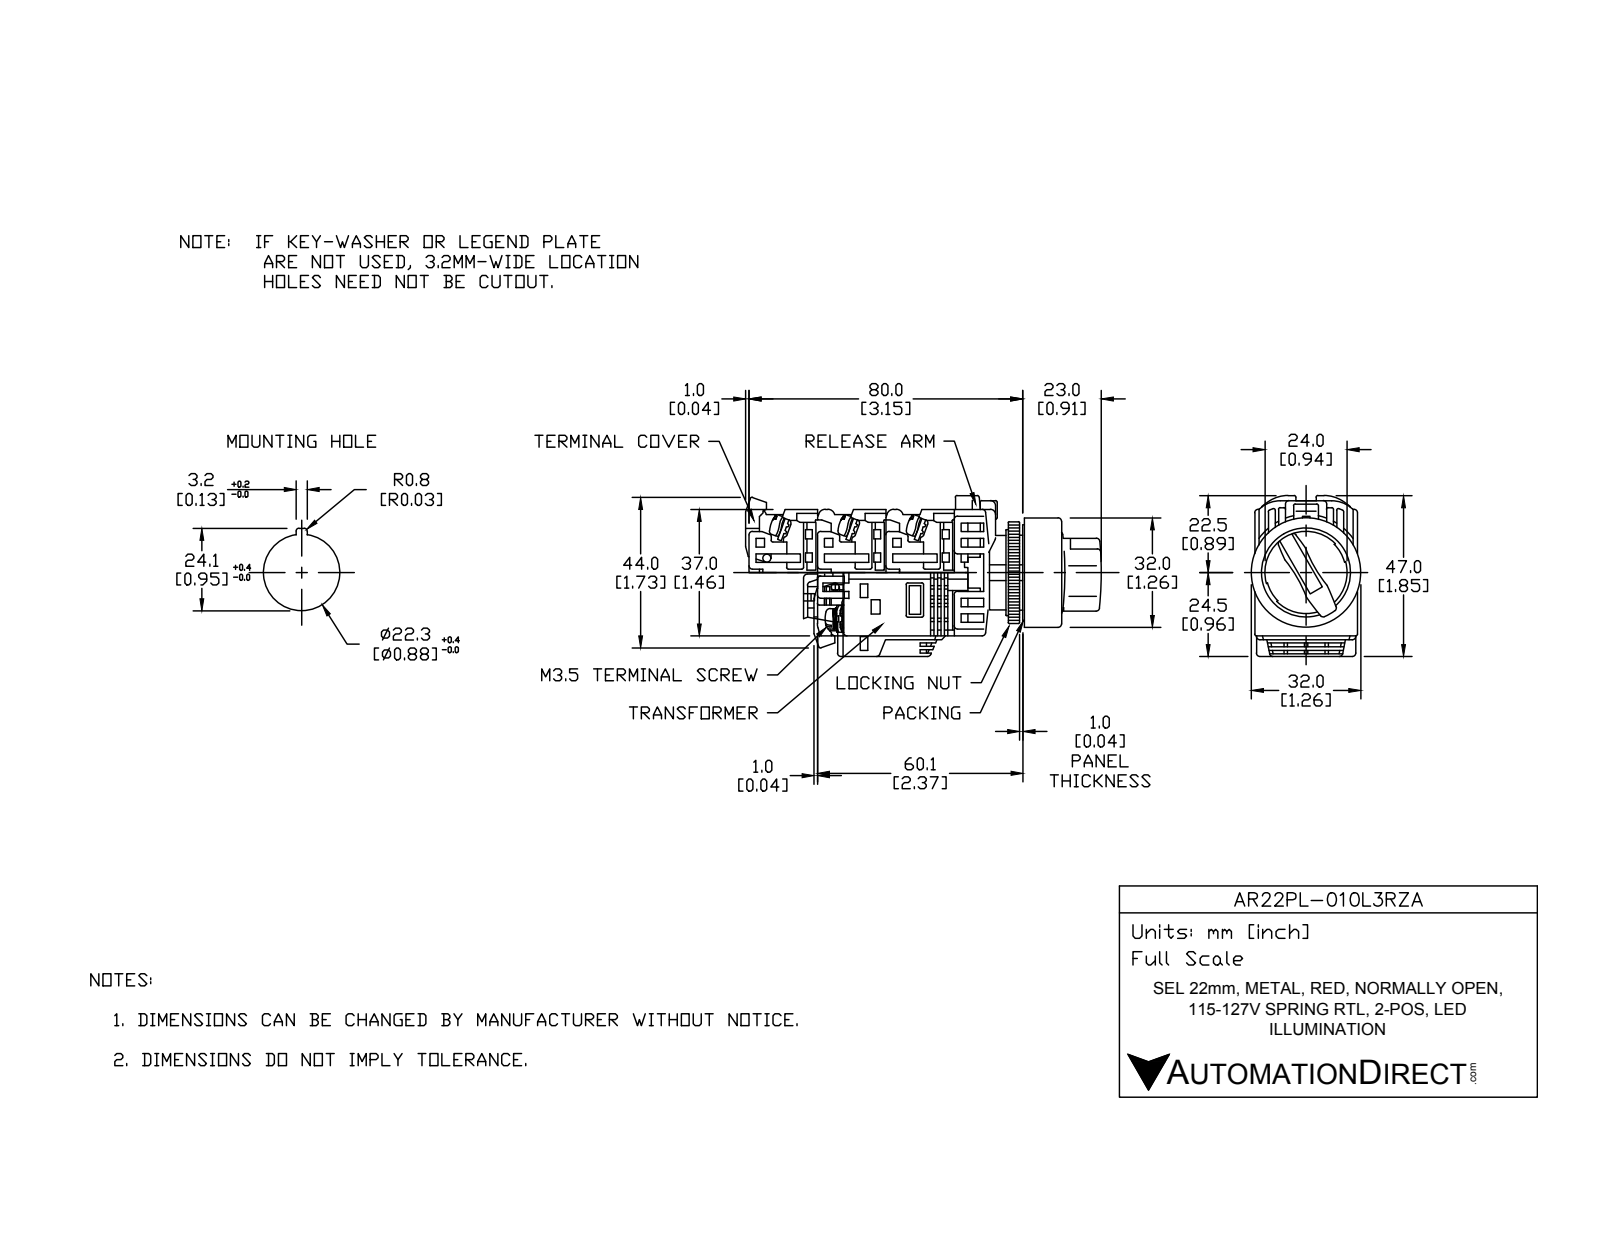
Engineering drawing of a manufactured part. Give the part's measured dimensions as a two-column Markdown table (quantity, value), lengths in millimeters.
| quantity | value |
| --- | --- |
| part name | AR22PL-010L3RZA |
| STEP written by | SolidWorks 2017 (AUTOMOTIVE_DESIGN) |
| units | millimeters |
| bodies | 18 solids, 462 faces (317 planar, 118 cylindrical, 27 other) |
| overall size | 84.5 × 43.81 × 32 |
| volume | 48 971 mm³ |
| surface area | 26 711 mm² |
| round holes (diameter × count) | 21.8 × 1, 22 × 1, 25 × 1, 31 × 1 |
| round bosses / shafts (diameter × count) | 5 × 4, 32 × 1, 30.5 × 1, 29.8 × 1, 24 × 1, 21.75 × 1, 17 × 1 |
| partial cylindrical surfaces (radius × count) | 0.5 × 39, 1.75 × 8, 1 × 6, 5 × 4, 4 × 2, 12 × 1, 16.59 × 1, 17.59 × 1 |
| main face-to-face distances | 1, 18, 29, 20, 3, 28.5, 0.5, 2, 21, 10 |
